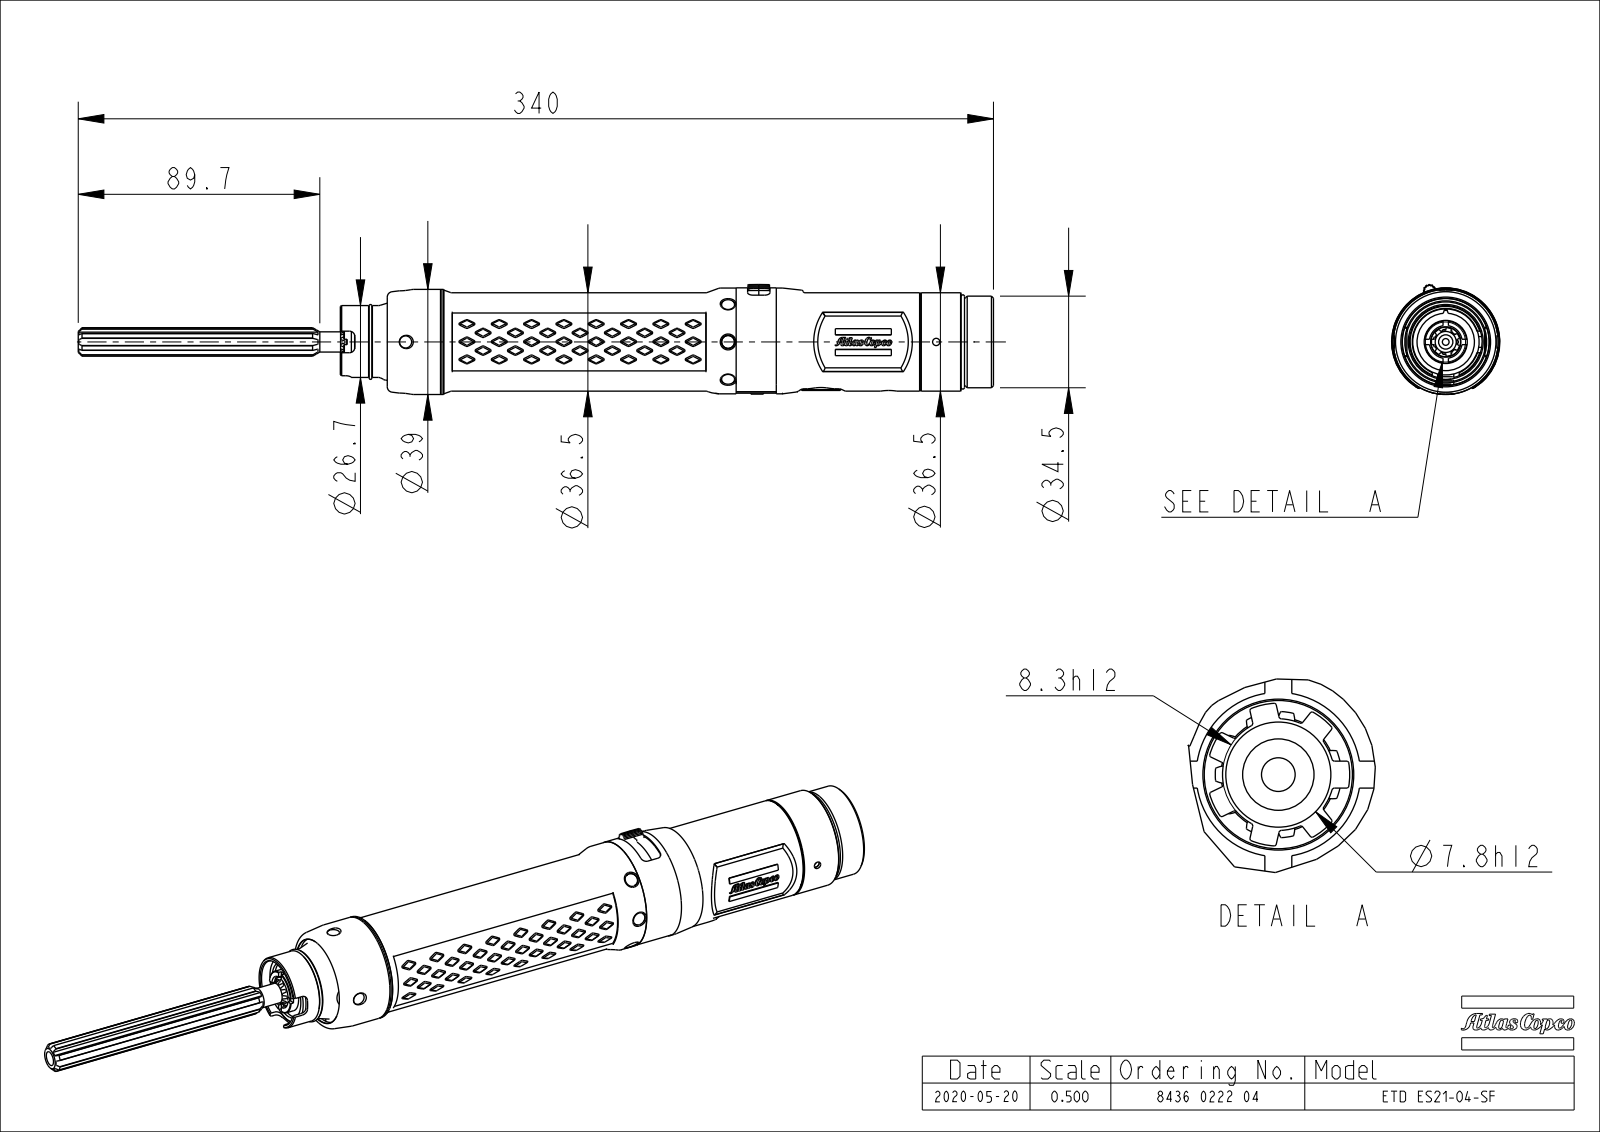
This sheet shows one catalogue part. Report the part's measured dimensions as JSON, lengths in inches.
{"part_name": "EXT_COMP_SW0066", "step_written_by": "CREO PARAMETRIC BY PTC INC, 2018100 (AP242_MANAGED_MODEL_BASED_3D_ENGINEERING_MIM_LF)", "units": "inches", "bodies": {"solids": 5, "faces": 4230, "planar": 1265, "cylindrical": 907, "other": 2058}, "overall_size": [13.377, 1.607, 1.581], "volume_in3": 13.37, "surface_area_in2": 135.9, "round_holes": [[0.104, 12], [0.129, 12], [0.142, 12], [0.165, 5], [0.197, 5], [0.024, 4], [0.031, 4], [0.067, 4], [0.098, 2], [0.106, 2], [0.177, 2], [0.217, 1]], "round_bosses_or_shafts": [[0.1, 6], [0.063, 6], [0.096, 4], [0.088, 4], [0.061, 4], [0.12, 3], [0.122, 2], [0.104, 2]], "partial_cylinders_radius": [[0.008, 50], [0.004, 32], [0.118, 32], [0.039, 25], [0.016, 20], [0.079, 18], [0.02, 13], [0.063, 12]], "face_to_face_distances": [0.079, 0.02, 1.324, 8.6, 7.276, 0.15, 0.02, 0.393, 0.931, 7.669], "hole_center_spacings": [0.231, 0.374, 0.204, 0.529, 0.667, 0.712, 0.739, 0.118]}
